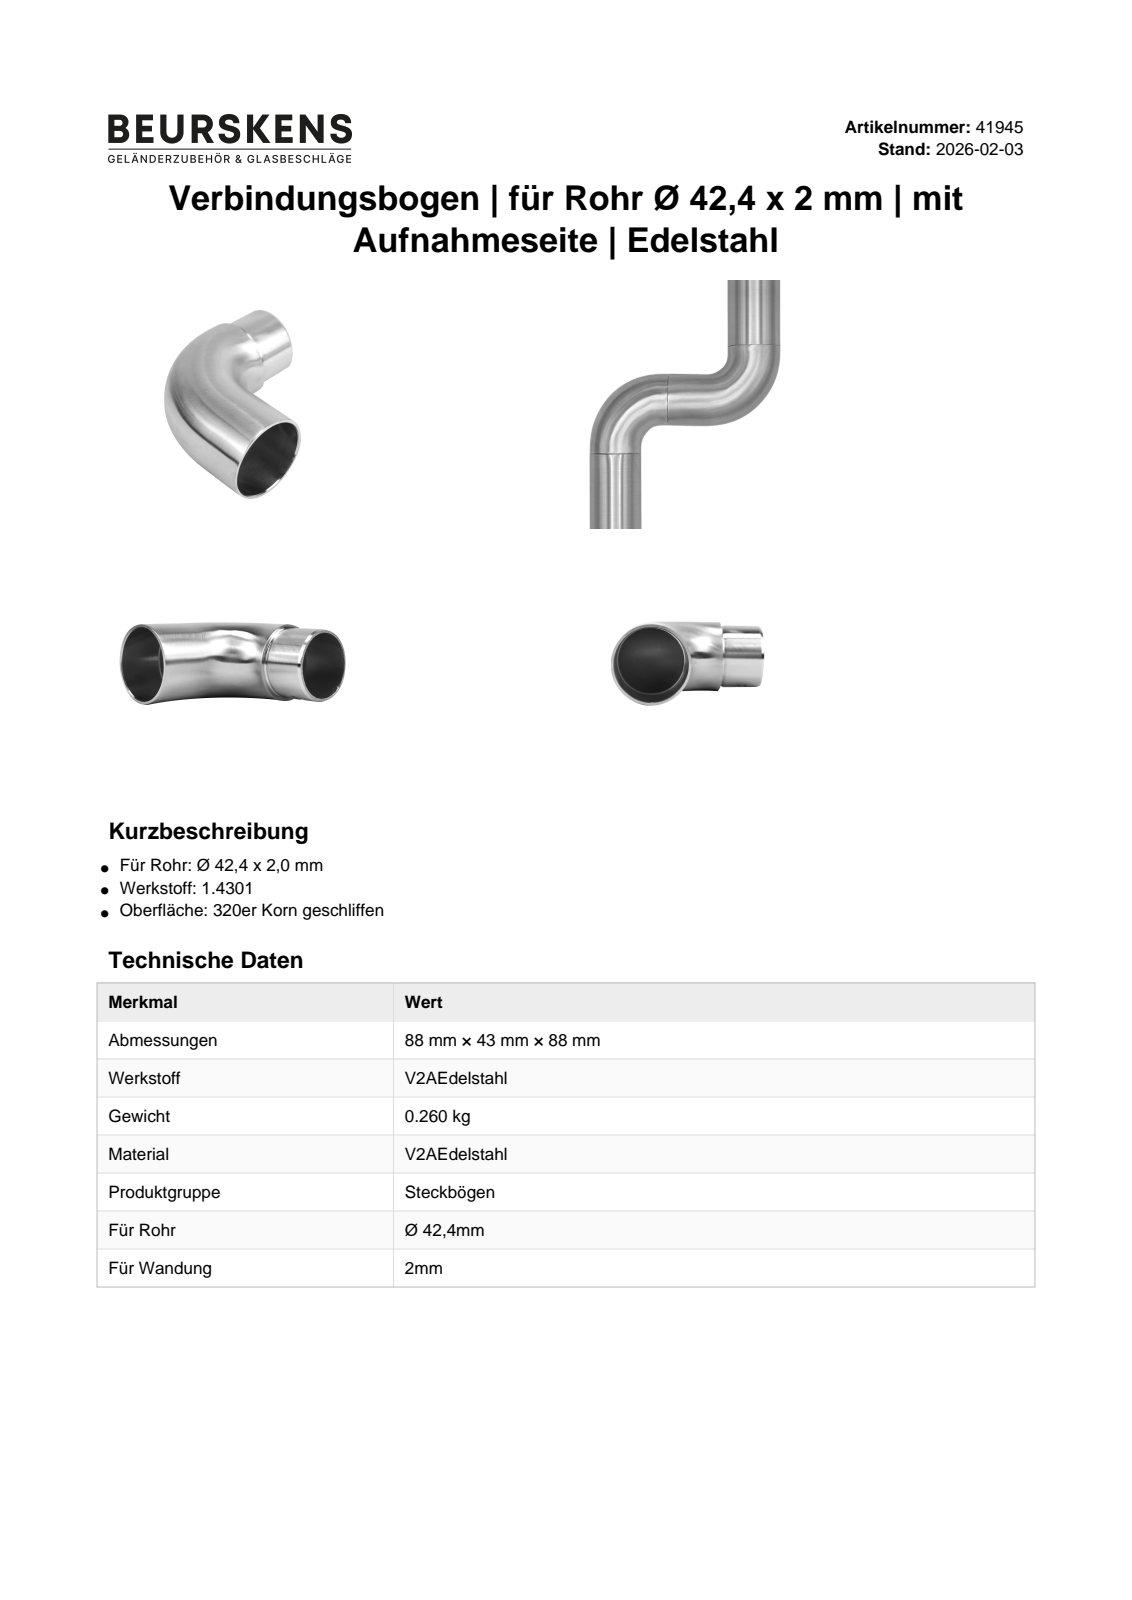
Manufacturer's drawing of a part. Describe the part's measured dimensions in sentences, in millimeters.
The part is named "41945". Its 3-D file was written by "Autodesk Inventor 2022 (AUTOMOTIVE_DESIGN)". It is 1 solid with 14 faces: 5 planar, 7 cylindrical and 2 other. Overall it measures 90 by 89 by 42.4 millimeters. Its volume is 42 024 cubic millimeters and its surface area 30 413 square millimeters. Round holes: 2 of diameter 36.4, 1 of diameter 32.4, 1 of diameter 38.4. Round bosses or shafts: 2 of diameter 42.4, 1 of diameter 38.4. The main face-to-face distances are 25, 28, 3, 20.
